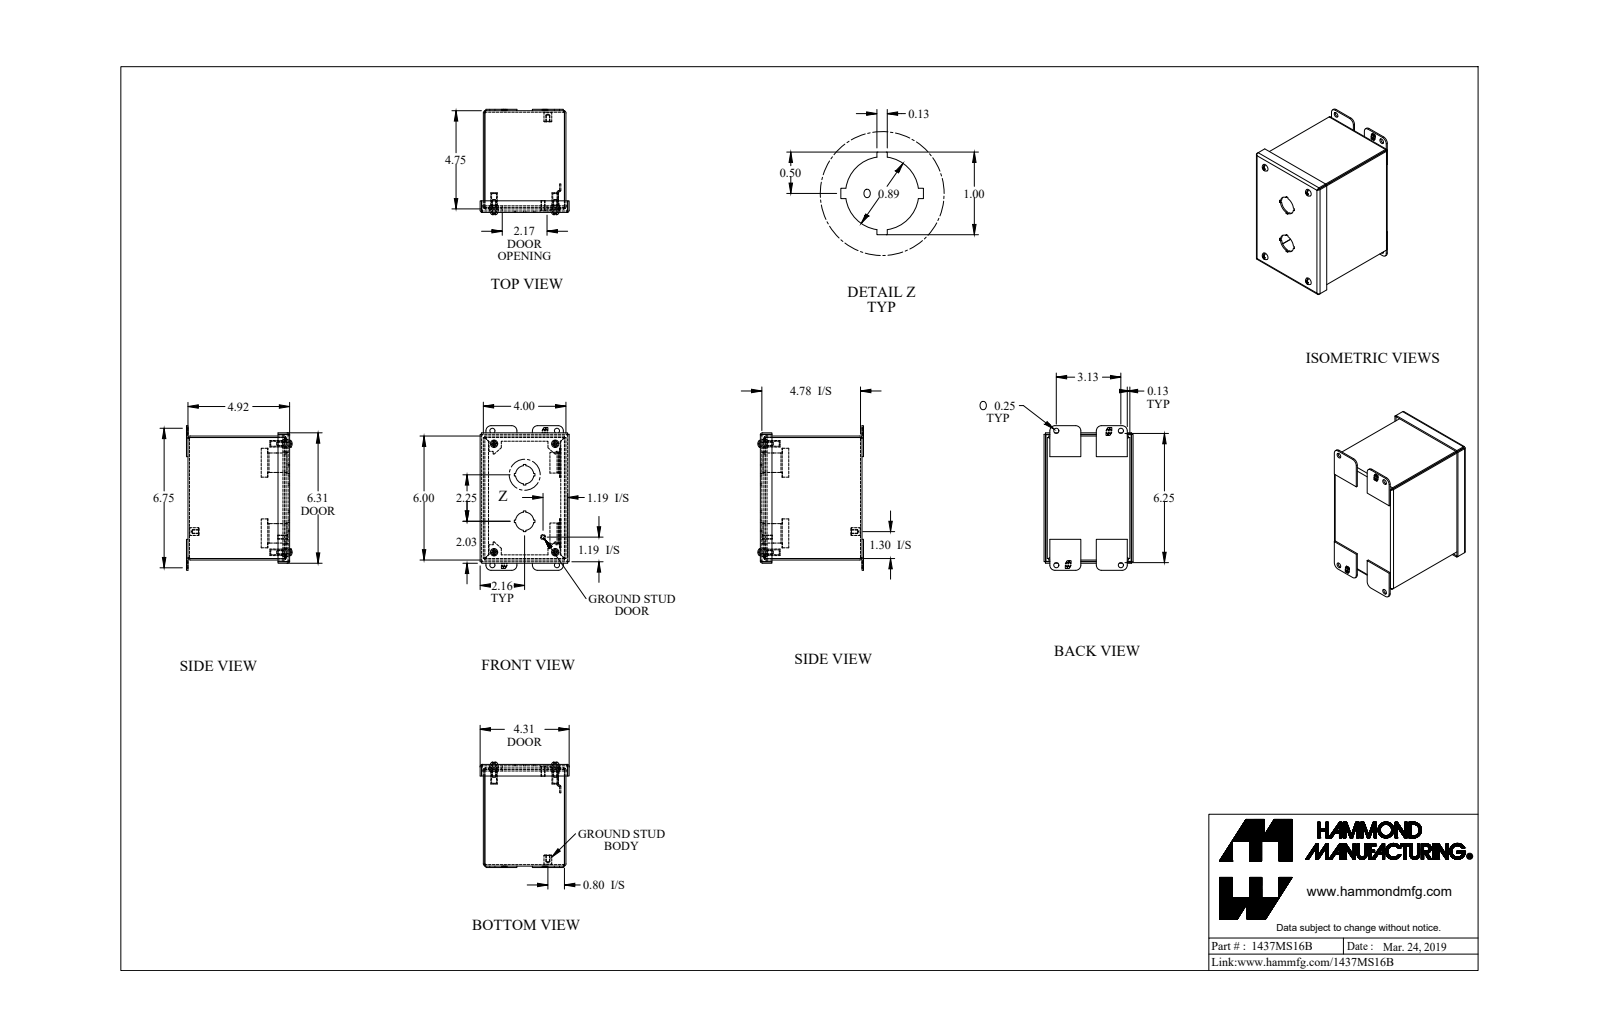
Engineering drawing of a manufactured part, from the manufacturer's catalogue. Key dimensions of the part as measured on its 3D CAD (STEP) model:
Part name (STEP PRODUCT): 1437MS16B_Default
STEP written by: SolidWorks 2019 (CONFIG_CONTROL_DESIGN)
Units: inches
Bodies: 23 solids, 637 faces (447 planar, 160 cylindrical, 30 other)
Overall size (bounding box): 7 × 5.104 × 4.312
Volume: 14.06 in³ · Surface area: 378.1 in²
Round holes (diameter × count): ⌀0.25 ×8, ⌀0.065 ×4, ⌀0.239 ×4, ⌀0.253 ×4, ⌀0.406 ×4, ⌀0.886 ×2, ⌀0.156 ×1
Round bosses / shafts (diameter × count): ⌀0.19 ×5, ⌀0.406 ×4, ⌀0.315 ×4, ⌀0.148 ×4, ⌀0.375 ×1, ⌀0.25 ×1
Partial cylindrical surfaces — rounded edges, fillets, slot ends (radius × count): R0.036 ×12, R0.108 ×12, R0.25 ×8, R0.029 ×4, R0.086 ×4, R0.125 ×4, R0.171 ×4
Main face-to-face distances: 0.072, 3.928, 4.85, 5.928, 4.922, 4, 3.856, 4.778, 0.156, 6
Hole centre spacings: 0.63, 2.961, 3.107, 4.031, 5.25, 5.875, 2.962, 2.107
